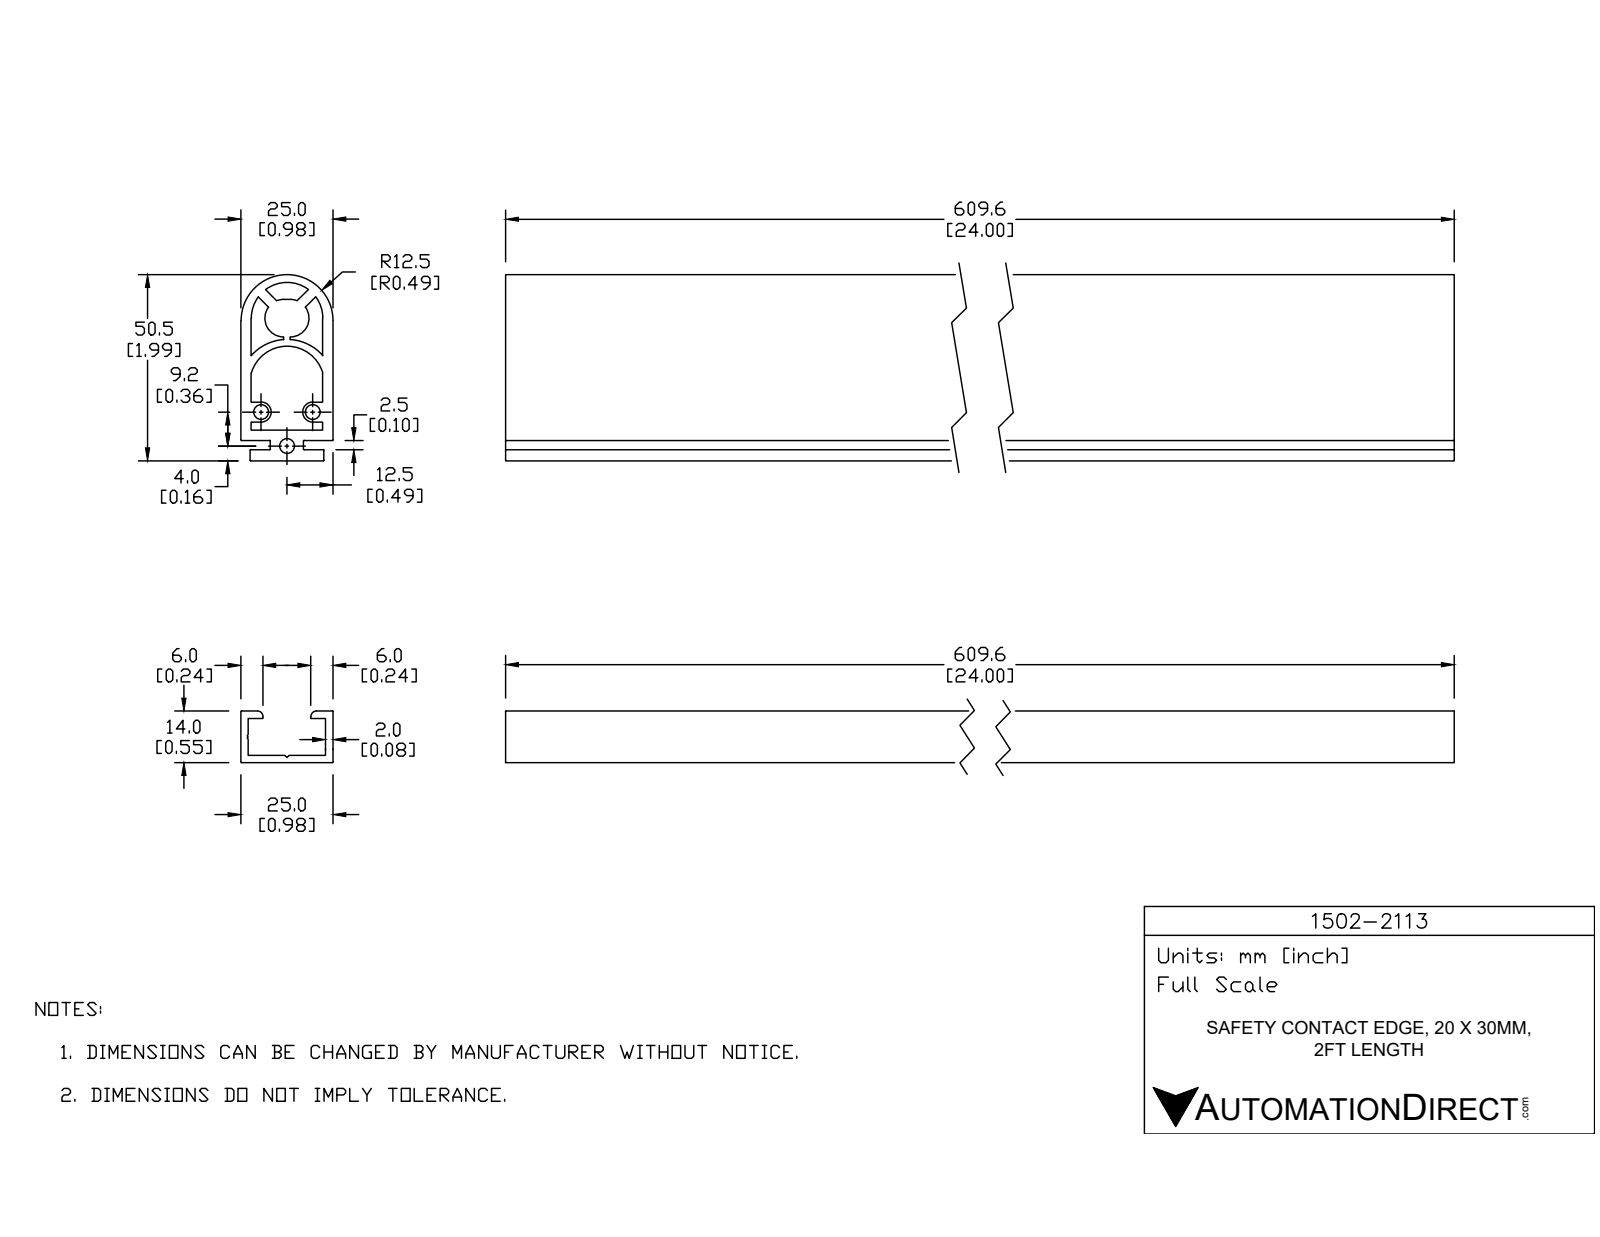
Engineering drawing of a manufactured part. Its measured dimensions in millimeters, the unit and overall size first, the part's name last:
Units: millimetres
Overall size (bounding box): 609.6 × 50.5 × 25
Round holes (diameter × count): ⌀4 ×3
Partial cylindrical surfaces — rounded edges, fillets, slot ends (radius × count): R0.2 ×10, R2.7 ×2, R5.12 ×2, R9.7 ×1, R10.11 ×1, R12.5 ×1, R12.9 ×1
Main face-to-face distances: 2.8, 22.2, 25, 19.4, 5.5, 8.3, 2.5, 3, 5.3, 2.79
Hole centre spacings: 11.57, 14
Volume: 358 449 mm³ · Surface area: 247 386 mm²
Bodies: 1 solid, 62 faces (31 planar, 31 cylindrical, 0 other)
Part name (STEP PRODUCT): 1502-2113
STEP written by: SolidWorks 2017 (AUTOMOTIVE_DESIGN)
